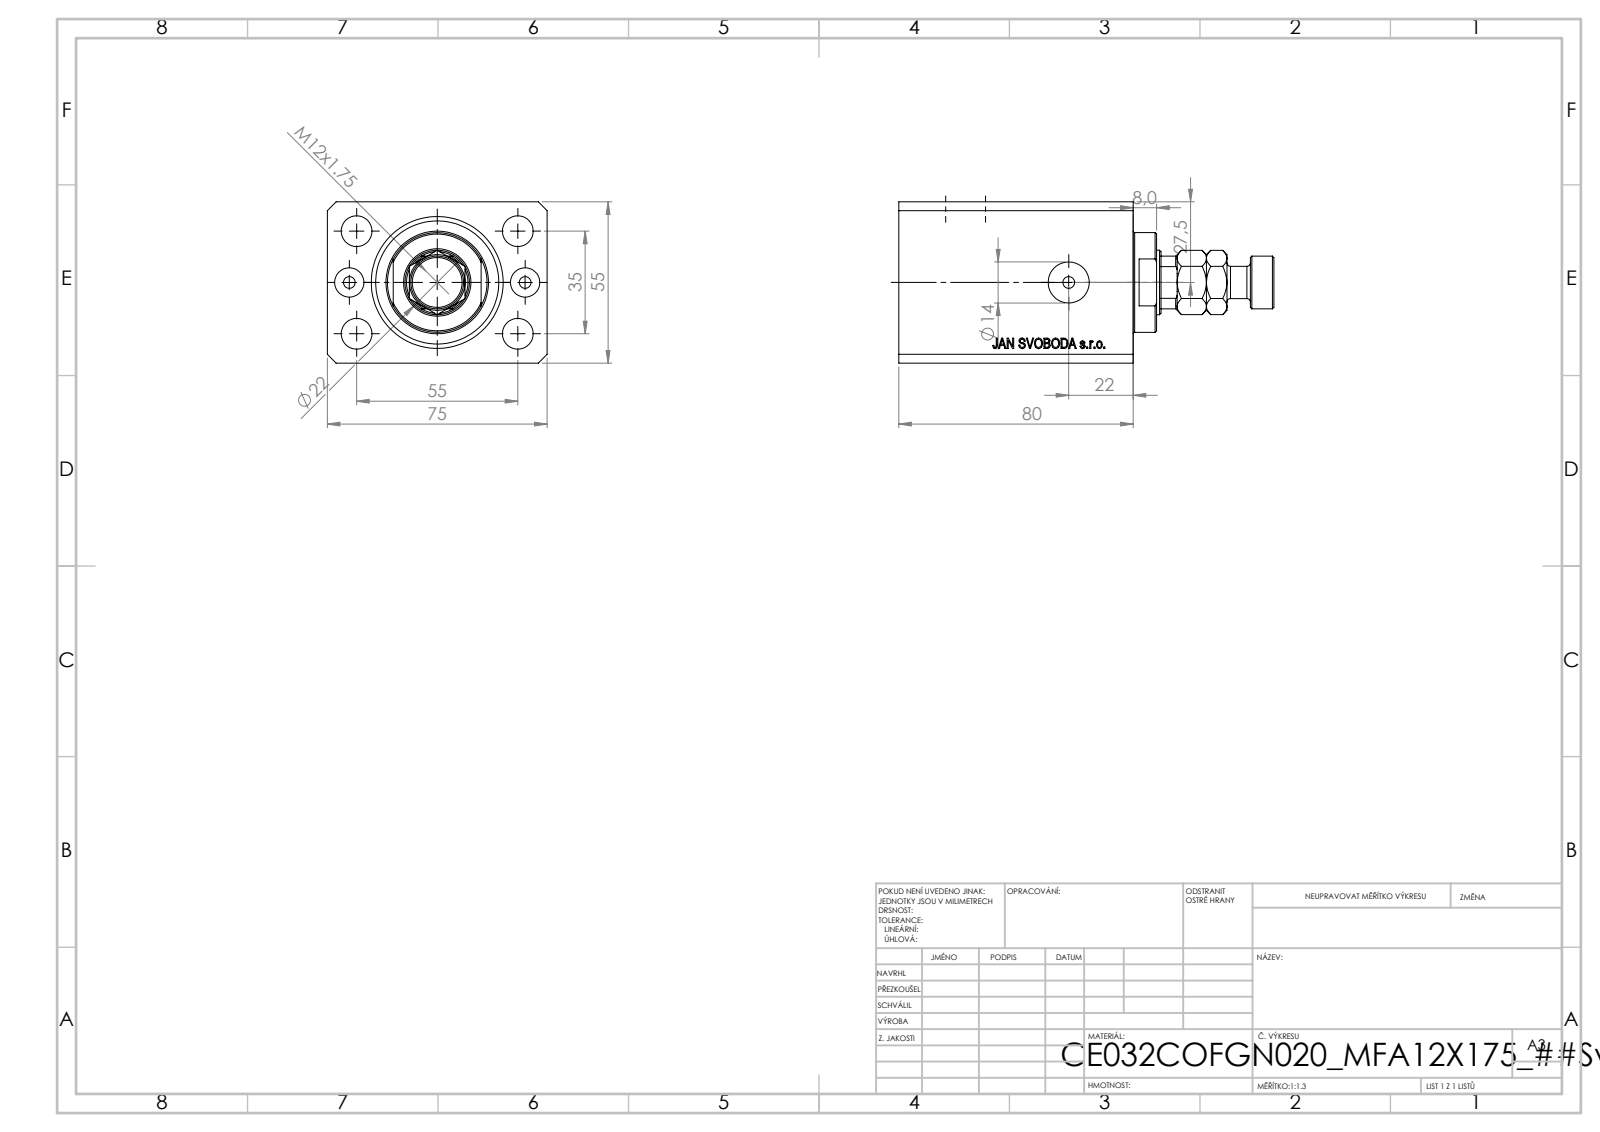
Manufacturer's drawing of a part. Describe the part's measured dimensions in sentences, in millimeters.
The part is named "V250CE_VC_C; V250CE_C_VCP; V250CE_C_Body; MFA". Its 3-D file was written by "SolidWorks 2019 (CONFIG_CONTROL_DESIGN)". It is 4 solids with 916 faces: 444 planar, 48 cylindrical and 424 other. Overall it measures 128 by 75 by 55 millimeters. Its volume is 304 678 cubic millimeters and its surface area 66 925 square millimeters. Round holes: 5 of diameter 10.5, 4 of diameter 4, 2 of diameter 10, 2 of diameter 14, 1 of diameter 22, 1 of diameter 32, 1 of diameter 45. Round bosses or shafts: 1 of diameter 34, 1 of diameter 18, 1 of diameter 11. Partial cylindrical surfaces (rounded edges, fillets, slot ends): 1 of radius 10.5. The main face-to-face distances are 55, 75, 15, 80, 65, 9.9, 55.1, 70.1, 87.66, 30. The hole center spacings are 17.68, 32.6, 60.1, 30, 35, 55, 65.19, 36.
